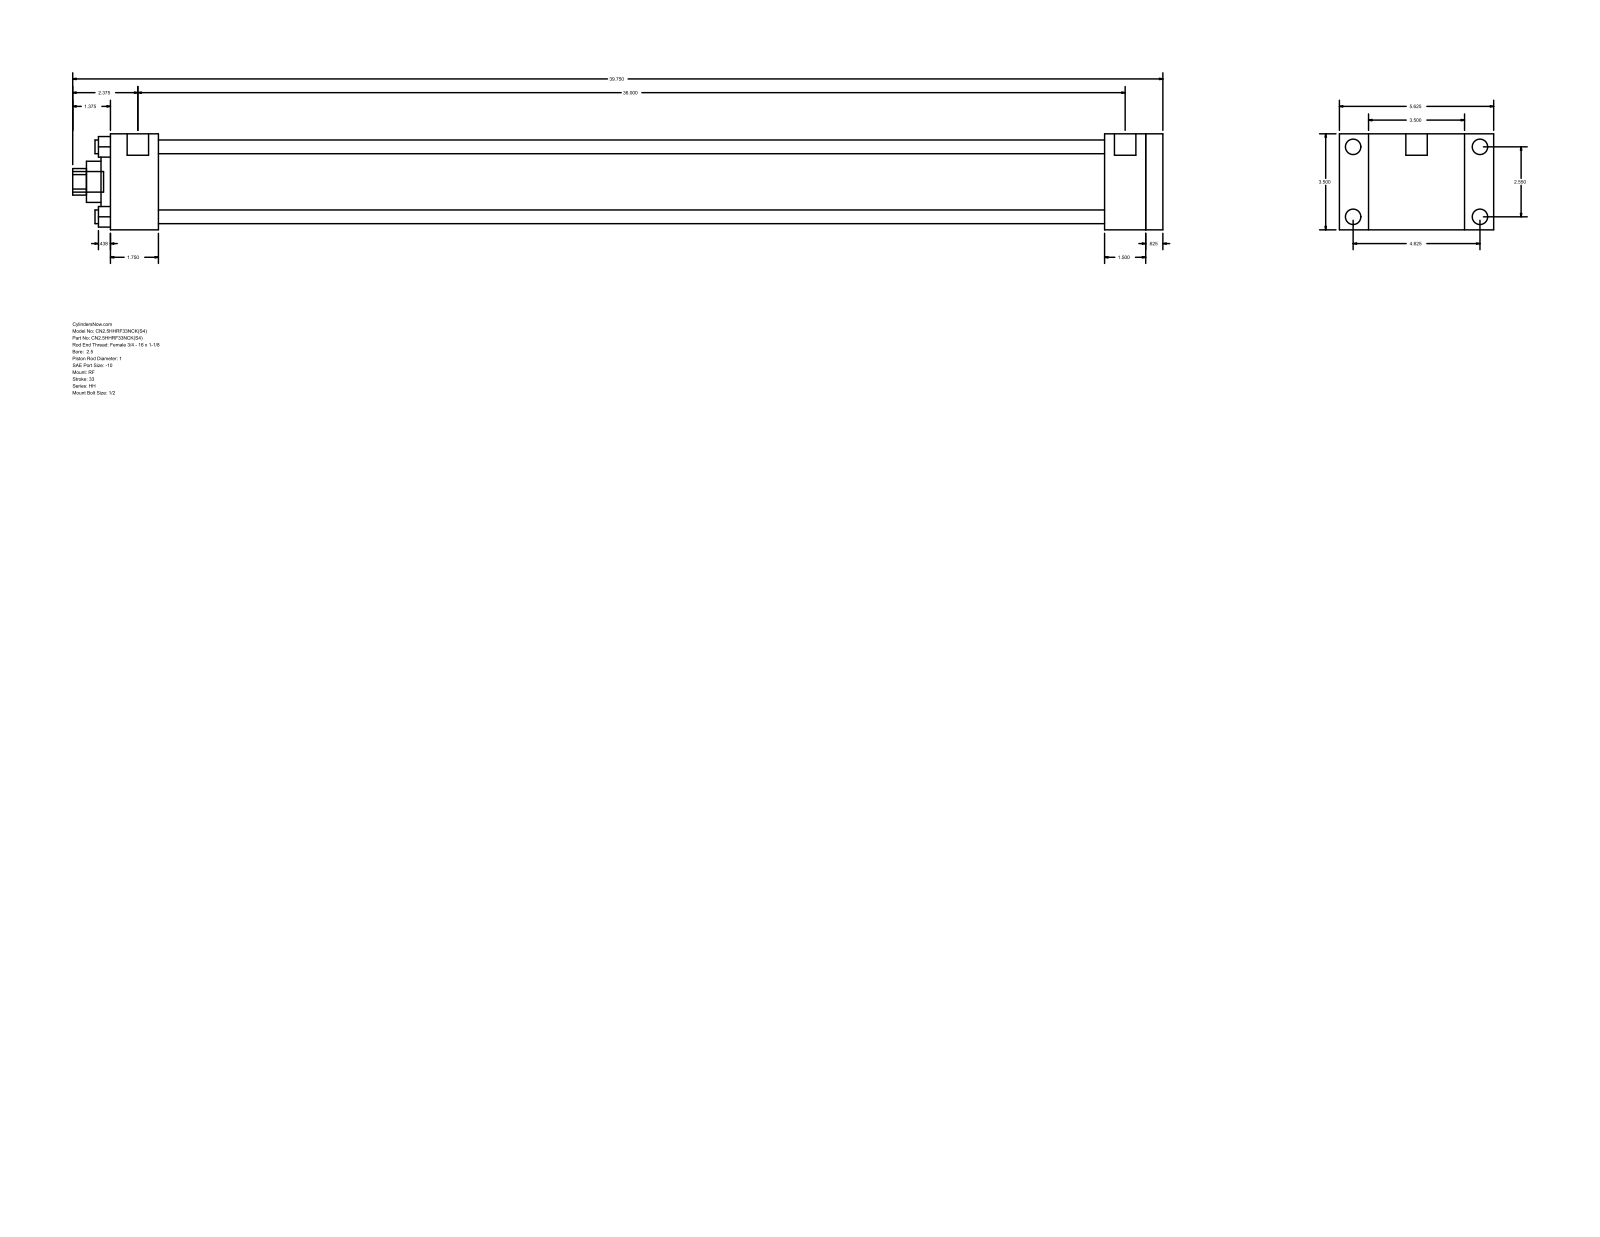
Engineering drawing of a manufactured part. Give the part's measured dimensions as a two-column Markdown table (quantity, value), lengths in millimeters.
| quantity | value |
| --- | --- |
| part name | HH_RF__0250_1 |
| STEP written by | GSSL Pune (CONFIG_CONTROL_DESIGN) |
| units | millimeters |
| bodies | 0 solids, 94 faces (65 planar, 29 cylindrical, 0 other) |
| overall size | 1009.65 × 142.88 × 88.9 |
| round holes (diameter × count) | 12.7 × 4, 25.4 × 1, 38.1 × 1, 60.33 × 1, 73.03 × 1 |
| round bosses / shafts (diameter × count) | 14.3 × 4, 5.56 × 4, 19.84 × 2, 19.05 × 1 |
| partial cylindrical surfaces (radius × count) | 12.29 × 1 |
| main face-to-face distances | 88.9, 15.88, 958.85, 974.73, 44.46, 914.39, 930.27, 920.75, 876.29, 38.1 |
| hole center spacings | 45.79, 64.76, 91.58 |
